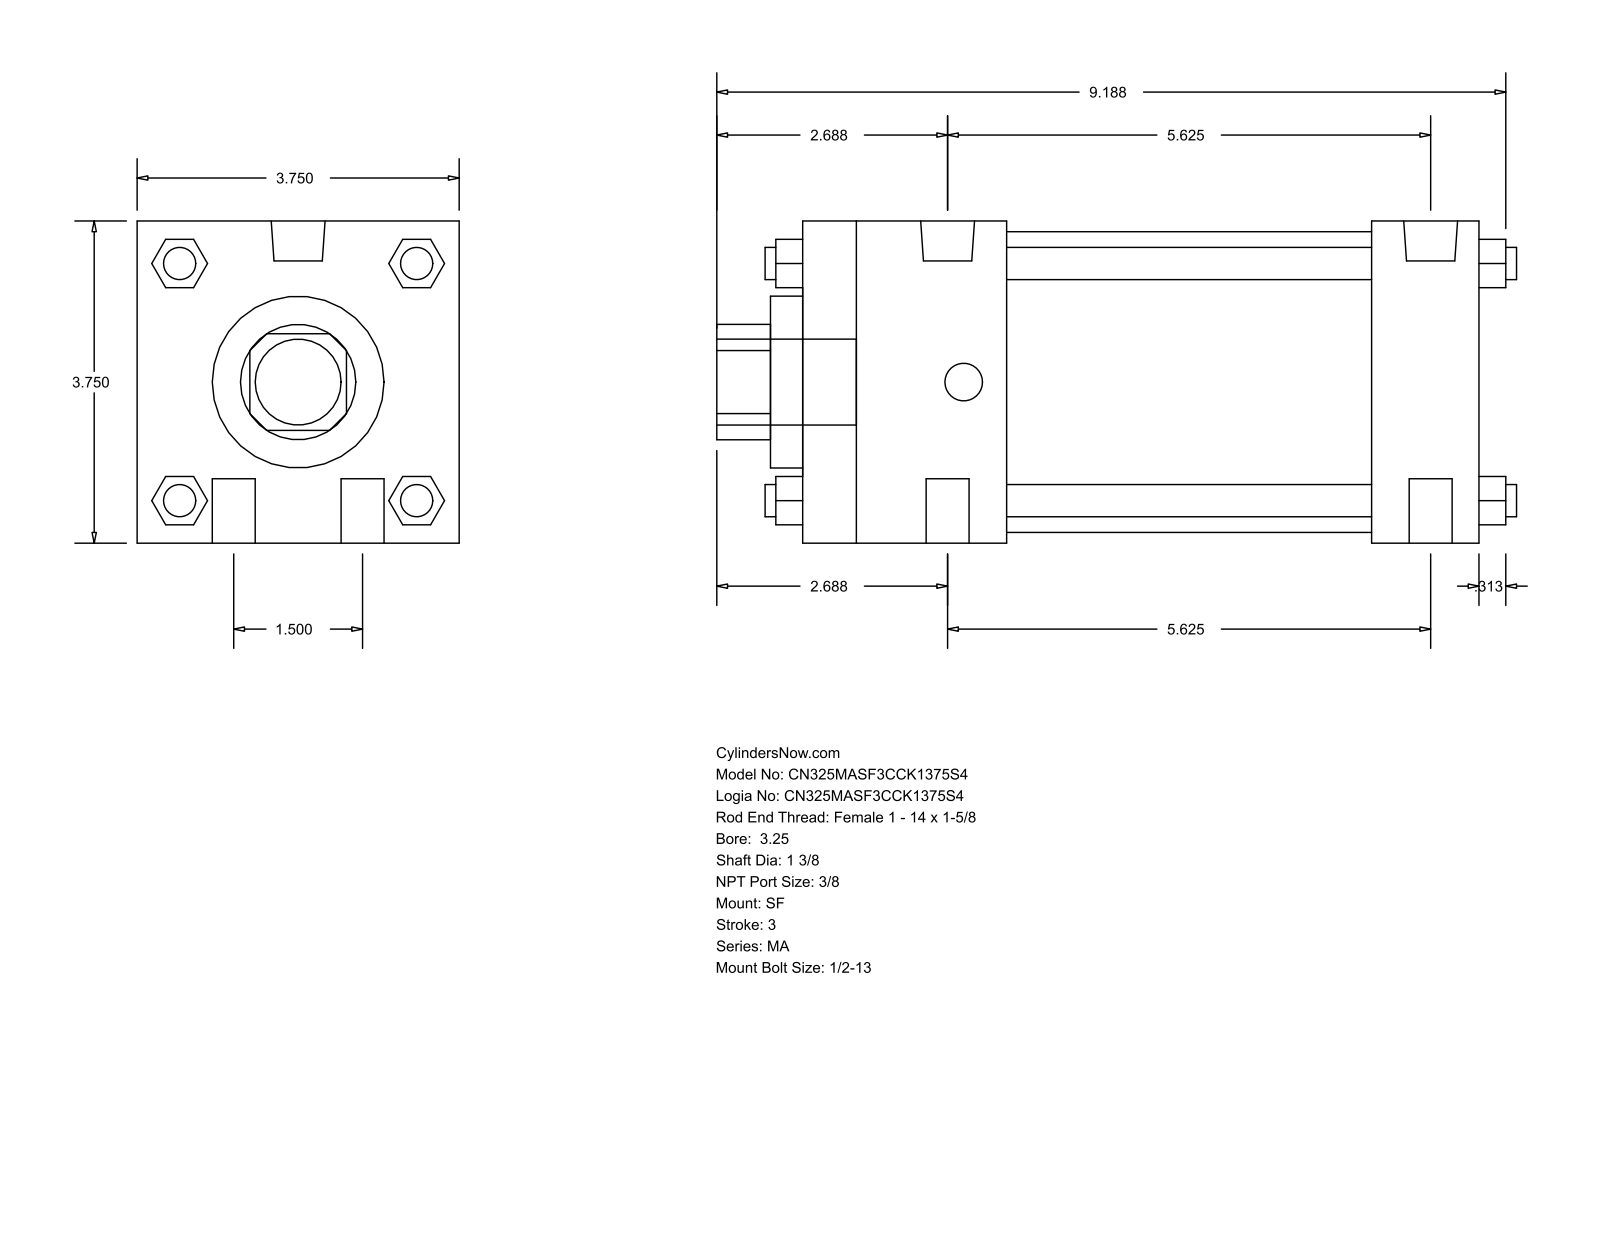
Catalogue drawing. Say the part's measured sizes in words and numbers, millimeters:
The part is named "MA_SF__0325_1.375". Its 3-D file was written by "GSSL Pune (CONFIG_CONTROL_DESIGN)". It is 0 solids with 124 faces: 94 planar, 30 cylindrical and 0 other. Overall it measures 236.54 by 95.25 by 95.25 millimeters. Round holes: 1 of diameter 34.92, 1 of diameter 50.8, 1 of diameter 88.9. Round bosses or shafts: 4 of diameter 12.7, 4 of diameter 9.53, 2 of diameter 15.93, 2 of diameter 11.11, 1 of diameter 25.4. Partial cylindrical surfaces (rounded edges, fillets, slot ends): 1 of radius 17.06. The main face-to-face distances are 95.24, 200.03, 168.28, 31.75, 60.32, 107.96, 139.71, 9.52, 69.84, 177.8.
